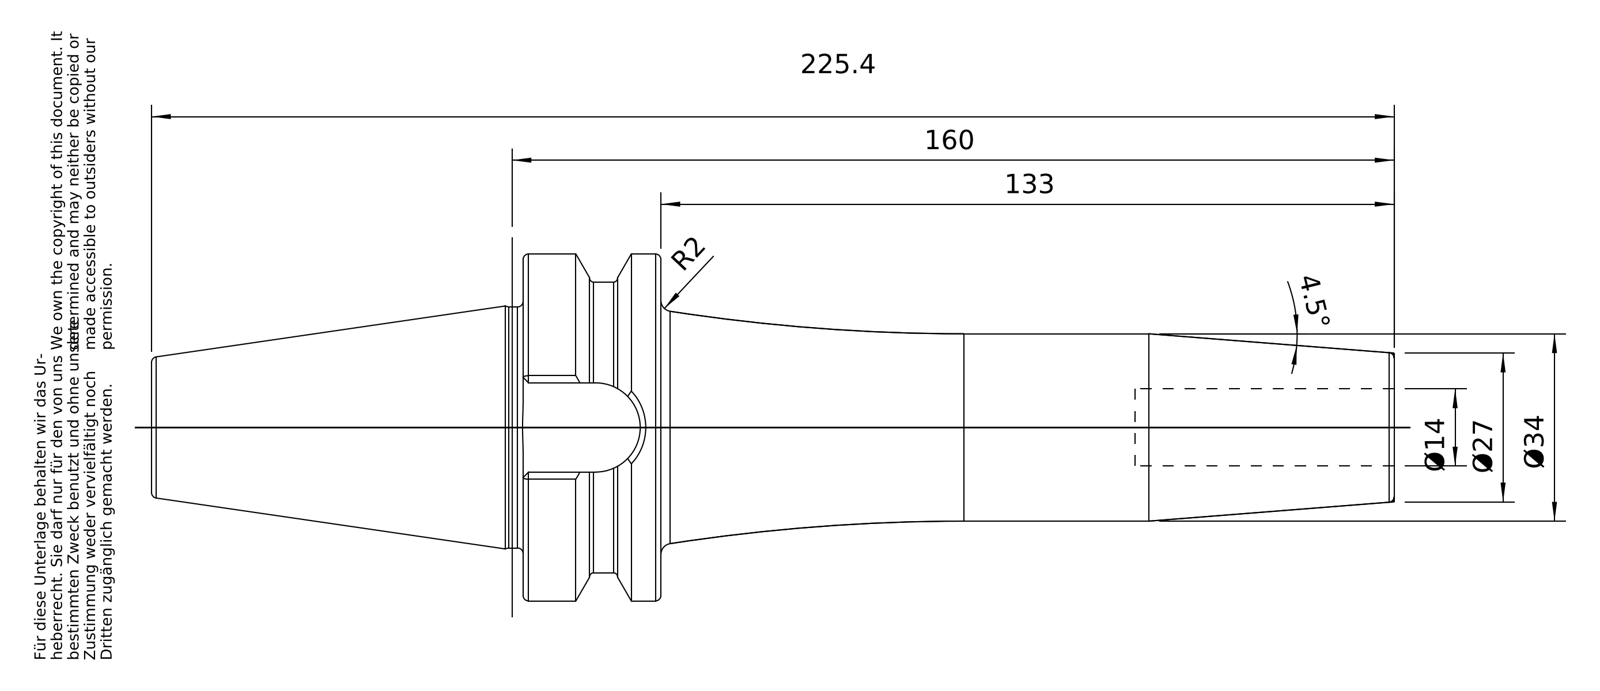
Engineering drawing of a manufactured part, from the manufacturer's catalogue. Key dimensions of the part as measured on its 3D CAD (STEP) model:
Part name (STEP PRODUCT): 40-642-14
STEP written by: PRO/ENGINEER BY PARAMETRIC TECHNOLOGY CORPORATION, 2010430 (CONFIG_CONTROL_DESIGN)
Units: millimetres
Bodies: 1 solid, 98 faces (26 planar, 22 cylindrical, 50 other)
Overall size (bounding box): 225.4 × 62.98 × 62.98
Volume: 241 129 mm³ · Surface area: 37 191 mm²
Round holes (diameter × count): ⌀13.84 ×1, ⌀14 ×1, ⌀17.01 ×1, ⌀17.5 ×1
Round bosses / shafts (diameter × count): ⌀62.98 ×1, ⌀52.75 ×1, ⌀43.75 ×1, ⌀34 ×1, ⌀16.01 ×1
Partial cylindrical surfaces — rounded edges, fillets, slot ends (radius × count): R8.1 ×1
Main face-to-face distances: 25, 158, 133, 44.9, 111, 86, 47, 16.2, 67.4, 92.4
